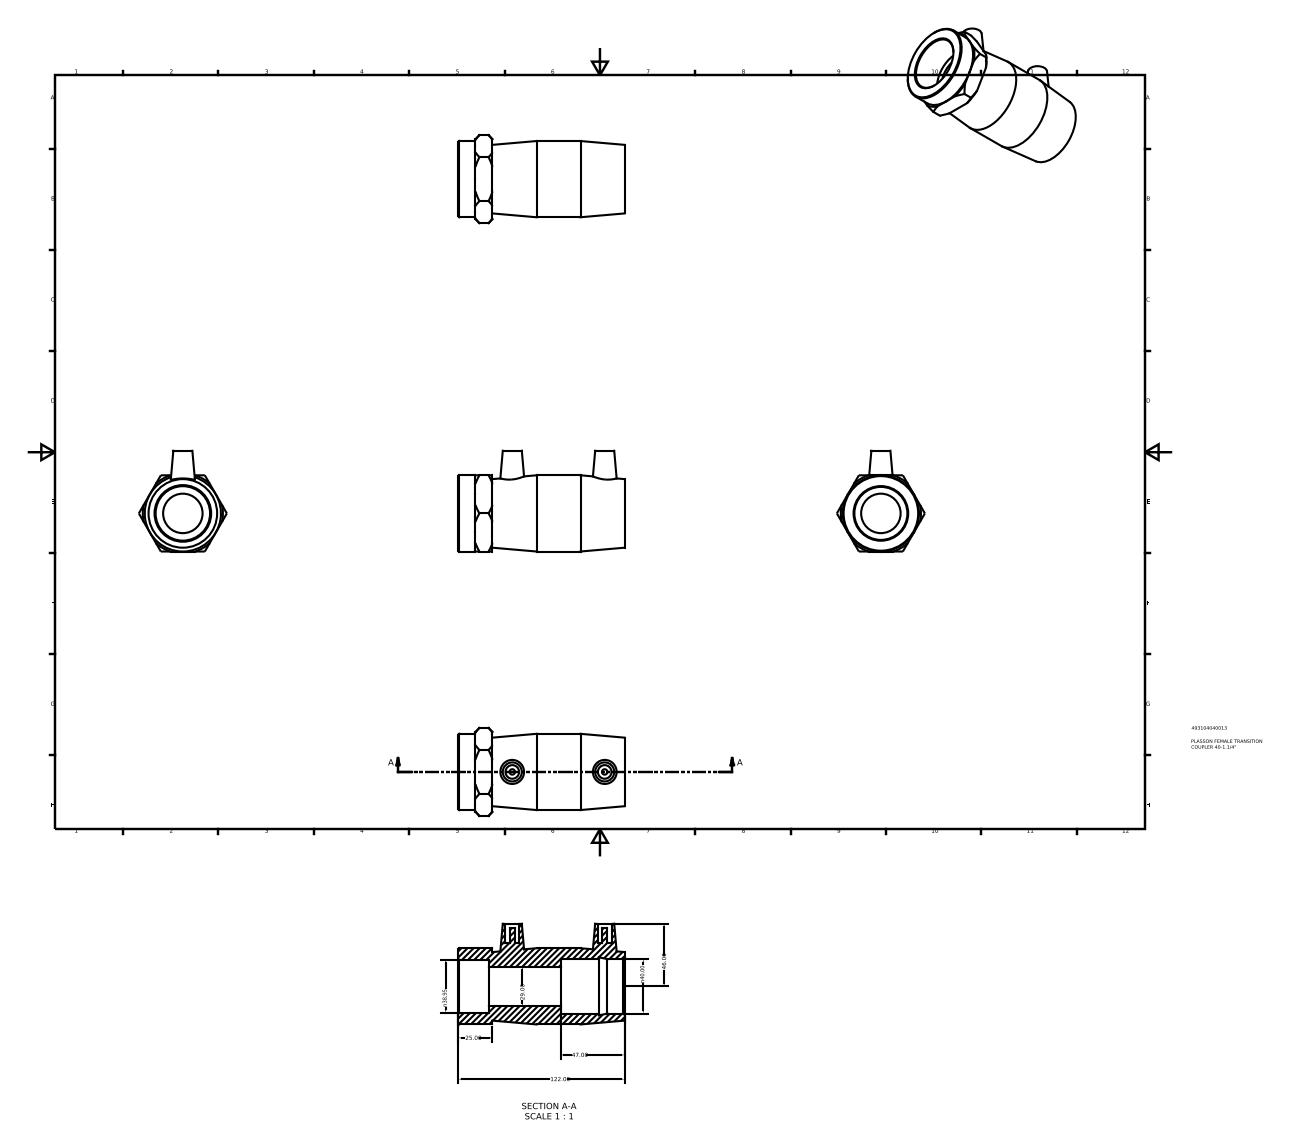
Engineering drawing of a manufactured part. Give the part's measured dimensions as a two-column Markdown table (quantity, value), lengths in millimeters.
| quantity | value |
| --- | --- |
| part name | 493104040013 |
| STEP written by | Autodesk Inventor 2015 (AUTOMOTIVE_DESIGN) |
| units | millimeters |
| bodies | 1 solid, 54 faces (24 planar, 10 cylindrical, 20 other) |
| overall size | 122 × 74 × 64.66 |
| volume | 172 747 mm³ |
| surface area | 41 614 mm² |
| round holes (diameter × count) | 10 × 2, 29 × 1, 38.95 × 1, 40 × 1 |
| round bosses / shafts (diameter × count) | 4 × 2, 56 × 1 |
| main face-to-face distances | 56, 122, 25, 97, 75, 50, 47, 22.5, 2.5, 52.5 |
| hole center spacings | 67.9 |
